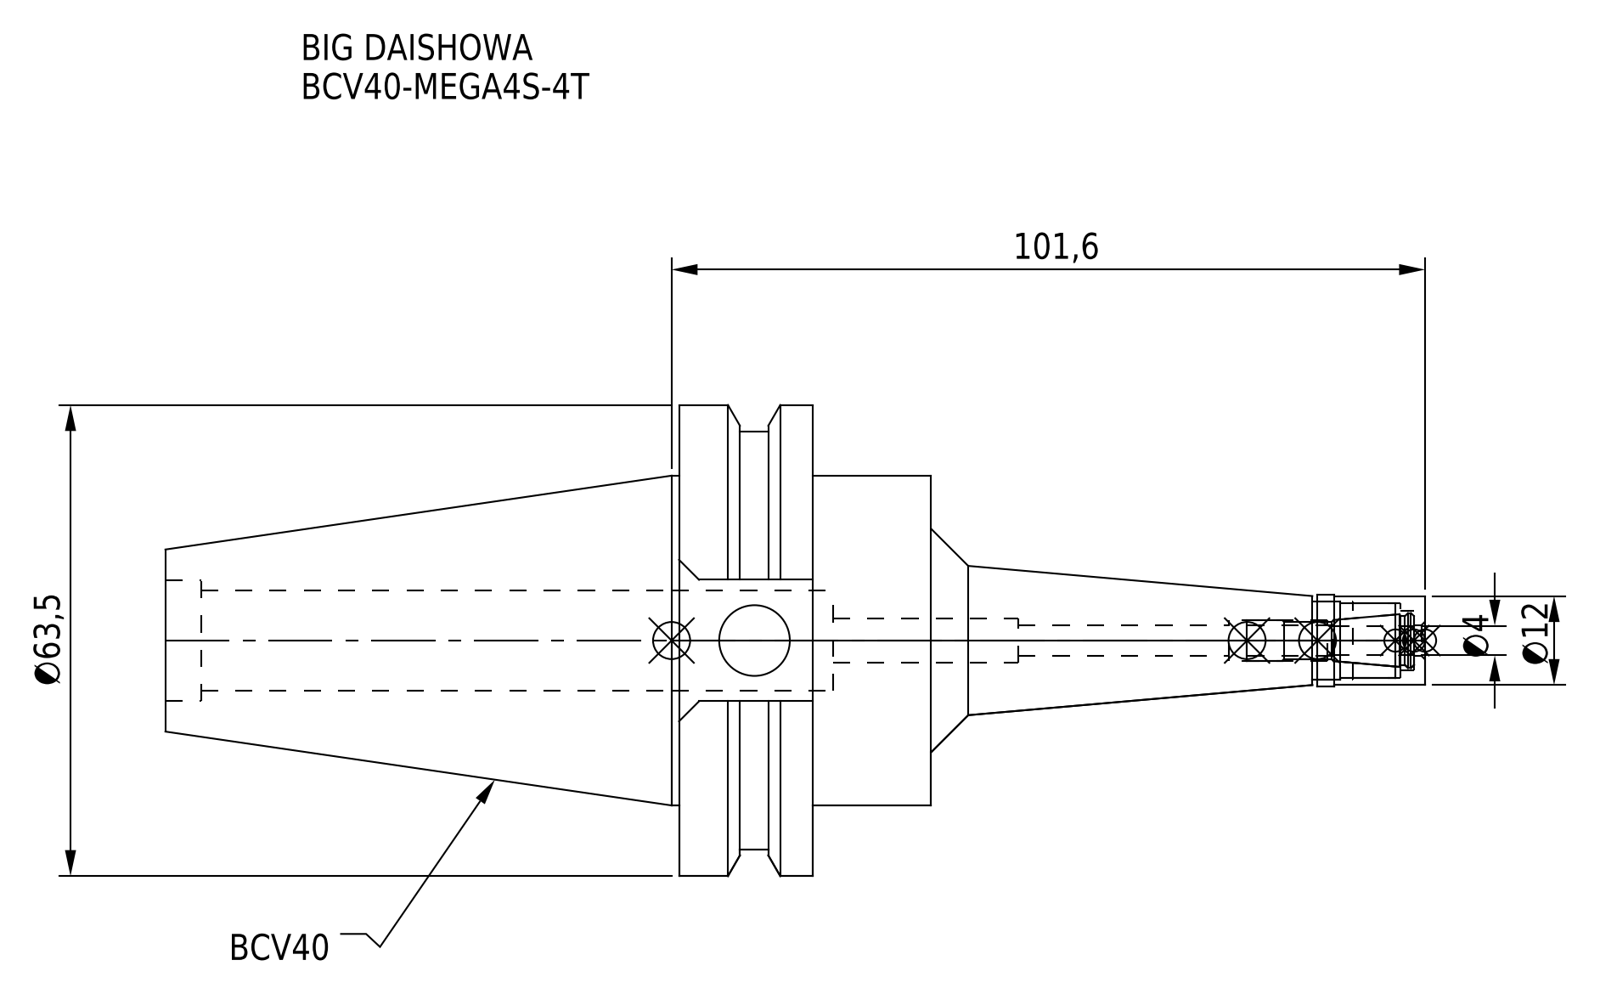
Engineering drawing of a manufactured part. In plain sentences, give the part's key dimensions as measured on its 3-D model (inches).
The part is named "MGN4S_1.stp; BCV40-MEGA4S-4T-040.stp; BCV40-MEGA4S-4T; BCV40-MEGA4S-4T-040-FreeParts (+3 more)". Its 3-D file was written by "SolidWorks 2019 (CONFIG_CONTROL_DESIGN)". It is 2 solids with 86 faces: 32 planar, 40 cylindrical and 14 other. Overall it measures 6.687 by 2.5 by 2.415 inches. Its volume is 8.551 cubic inches and its surface area 43.62 square inches. Round holes: 1 of diameter 0.161, 1 of diameter 0.165, 1 of diameter 0.213, 1 of diameter 0.236, 1 of diameter 0.315, 1 of diameter 0.375, 1 of diameter 0.394, 1 of diameter 0.413, 1 of diameter 0.535, 1 of diameter 0.643. Round bosses or shafts: 1 of diameter 2.5, 1 of diameter 2.219, 1 of diameter 1.75, 1 of diameter 0.484, 1 of diameter 0.472. The main face-to-face distances are 0.711, 0.628, 1.339, 4.065, 3.437, 2.726, 1.872, 0.645, 0.522, 0.106.
